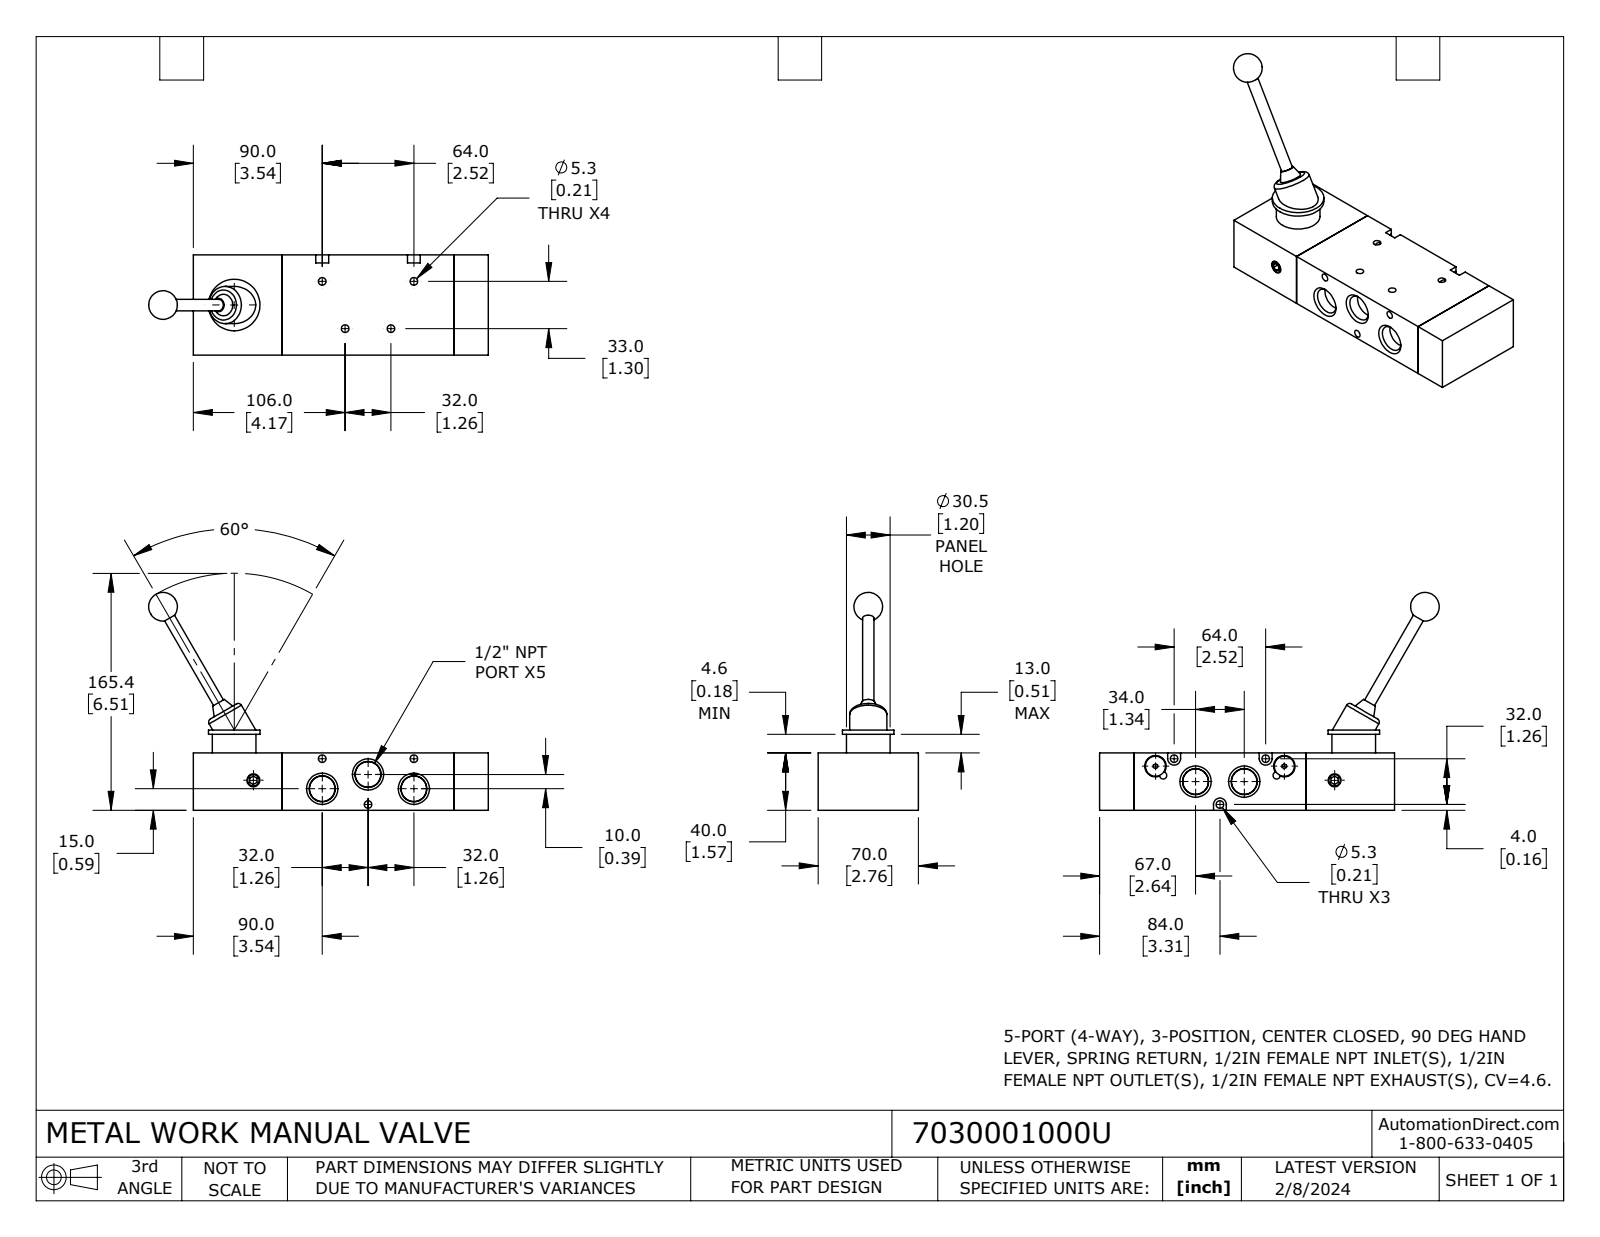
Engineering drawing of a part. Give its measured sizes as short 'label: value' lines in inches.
name: 7030001000U
written by: SolidWorks 2023 (CONFIG_CONTROL_DESIGN)
unit: in
bodies: 3 solids, 155 faces (72 planar, 57 cylindrical, 26 other)
size: 9.339 × 5.988 × 2.756
volume: 35.65 in³; area: 120.8 in²
holes: 7× ⌀0.209, 2× ⌀0.587, 1× ⌀0.354
bosses: 2× ⌀0.551, 1× ⌀1.417, 1× ⌀1.201, 1× ⌀1.024, 1× ⌀0.315, 1× ⌀0.313
rounds: 3× R0.177, 2× R0.098
face distances: 1.575, 2.756, 4.724, 0.945, 5.669, 8.11, 7.165, 2.441, 0.354, 2.402
hole spacings: 0.552, 1.444, 1.781, 2.061, 2.293, 2.52, 3.039, 1.26
